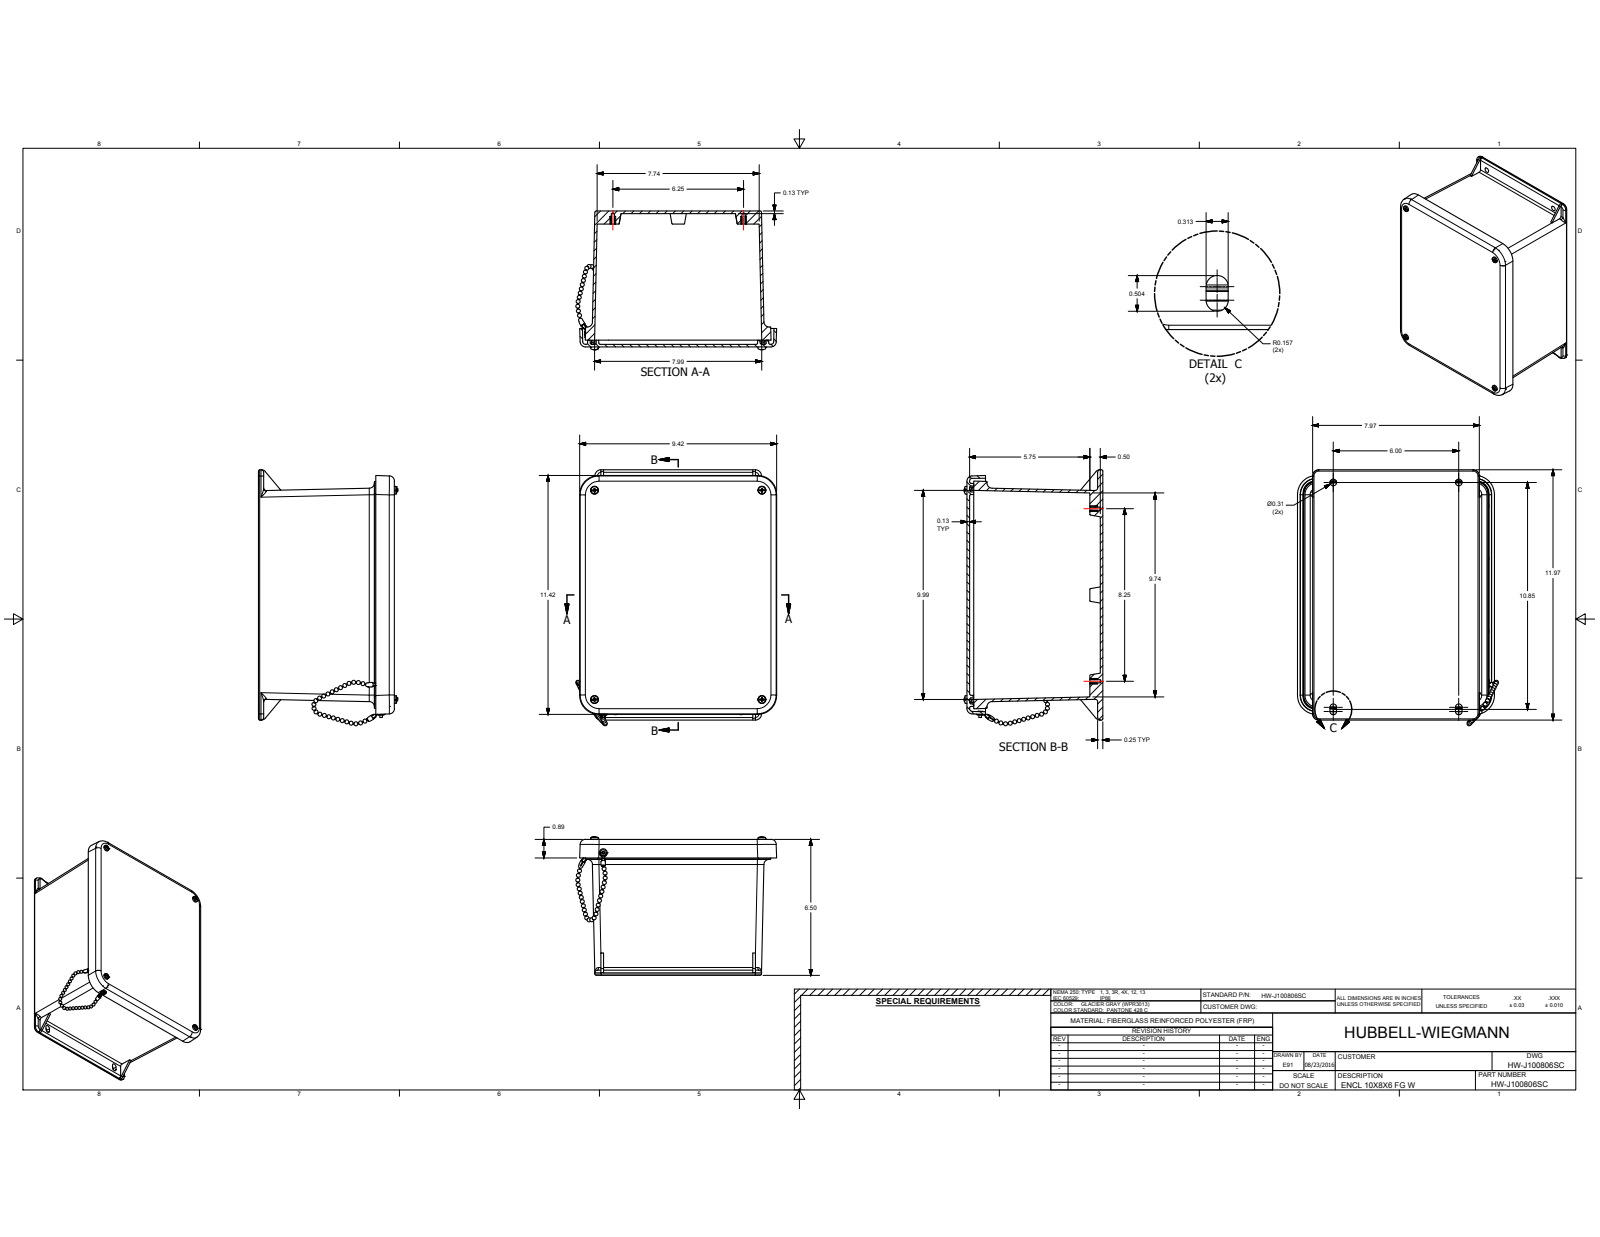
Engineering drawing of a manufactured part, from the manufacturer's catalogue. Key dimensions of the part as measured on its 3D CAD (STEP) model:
Part name (STEP PRODUCT): J100806W_STP; WPJ100806HBOX; WPJ100806WU; WPJ100806WCVR (+8 more)
STEP written by: Autodesk Inventor 2017 (AUTOMOTIVE_DESIGN)
Units: millimetres
Bodies: 29 solids, 1274 faces (321 planar, 427 cylindrical, 526 other)
Overall size (bounding box): 310.83 × 243.9 × 168.35
Volume: 1 243 000 mm³ · Surface area: 639 594 mm²
Round holes (diameter × count): ⌀3.86 ×12, ⌀4.04 ×12, ⌀3.56 ×5, ⌀9.52 ×4, ⌀2.64 ×2, ⌀4.76 ×2, ⌀7.95 ×2, ⌀3.2 ×1
Round bosses / shafts (diameter × count): ⌀6.86 ×12, ⌀4.83 ×4, ⌀3.97 ×4, ⌀9.52 ×2, ⌀3.17 ×2, ⌀7.19 ×1
Partial cylindrical surfaces — rounded edges, fillets, slot ends (radius × count): R1.59 ×34, R0.79 ×26, R1.6 ×20, R3.17 ×18, R1 ×16, R7.62 ×12, R6.35 ×10, R1.57 ×8
Main face-to-face distances: 3.18, 165.02, 3.11, 3.12, 161.84, 158.67, 3.17, 161.85, 5.08, 156.76
Hole centre spacings: 152.4, 221.09, 27.13, 31.43, 31.91, 63.5, 82.57, 104.02
